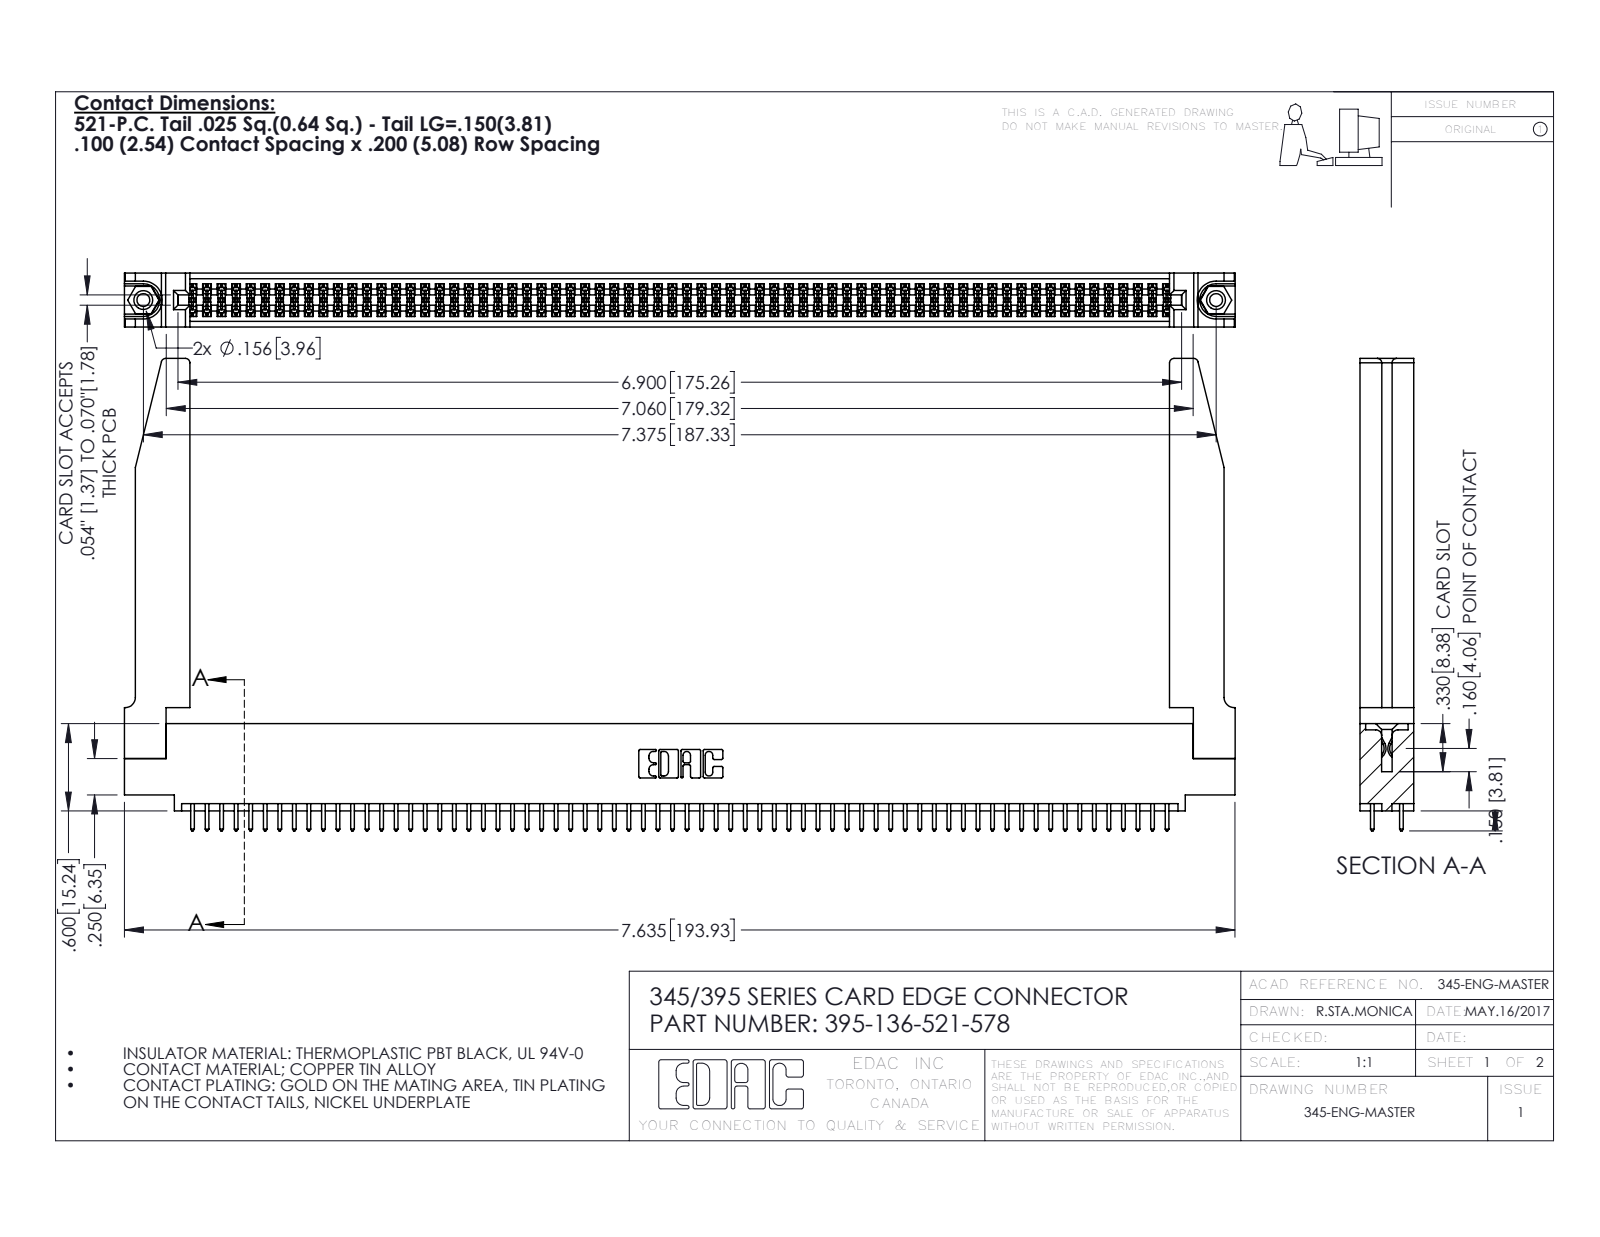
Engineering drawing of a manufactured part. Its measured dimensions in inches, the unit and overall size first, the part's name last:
Units: inches
Overall size (bounding box): 7.636 × 3.247 × 0.37
Round holes (diameter × count): ⌀0.089 ×2, ⌀0.125 ×2, ⌀0.156 ×2, ⌀0.064 ×1
Round bosses / shafts (diameter × count): ⌀0.155 ×2
Partial cylindrical surfaces — rounded edges, fillets, slot ends (radius × count): R0.006 ×204, R0.01 ×136, R0.01 ×22, R0.03 ×8, R0.007 ×6, R0.031 ×6, R0.026 ×3, R0.014 ×2
Main face-to-face distances: 0.072, 0.298, 0.37, 0.098, 0.272, 0.025, 0.2, 0.225, 0.175, 0.149
Hole centre spacings: 0.27, 7.139, 7.375
Volume: 1.631 in³ · Surface area: 54.39 in²
Bodies: 141 solids, 7164 faces (4714 planar, 2398 cylindrical, 52 other)
Part name (STEP PRODUCT): 345 Part_0.110 Offset - 0.156 Dia-TH; 395-136-521-578; 345-250-001_345-250-001-102; 345-220-078_345-220-078 (+1 more)
STEP written by: SolidWorks 2016 (CONFIG_CONTROL_DESIGN)
